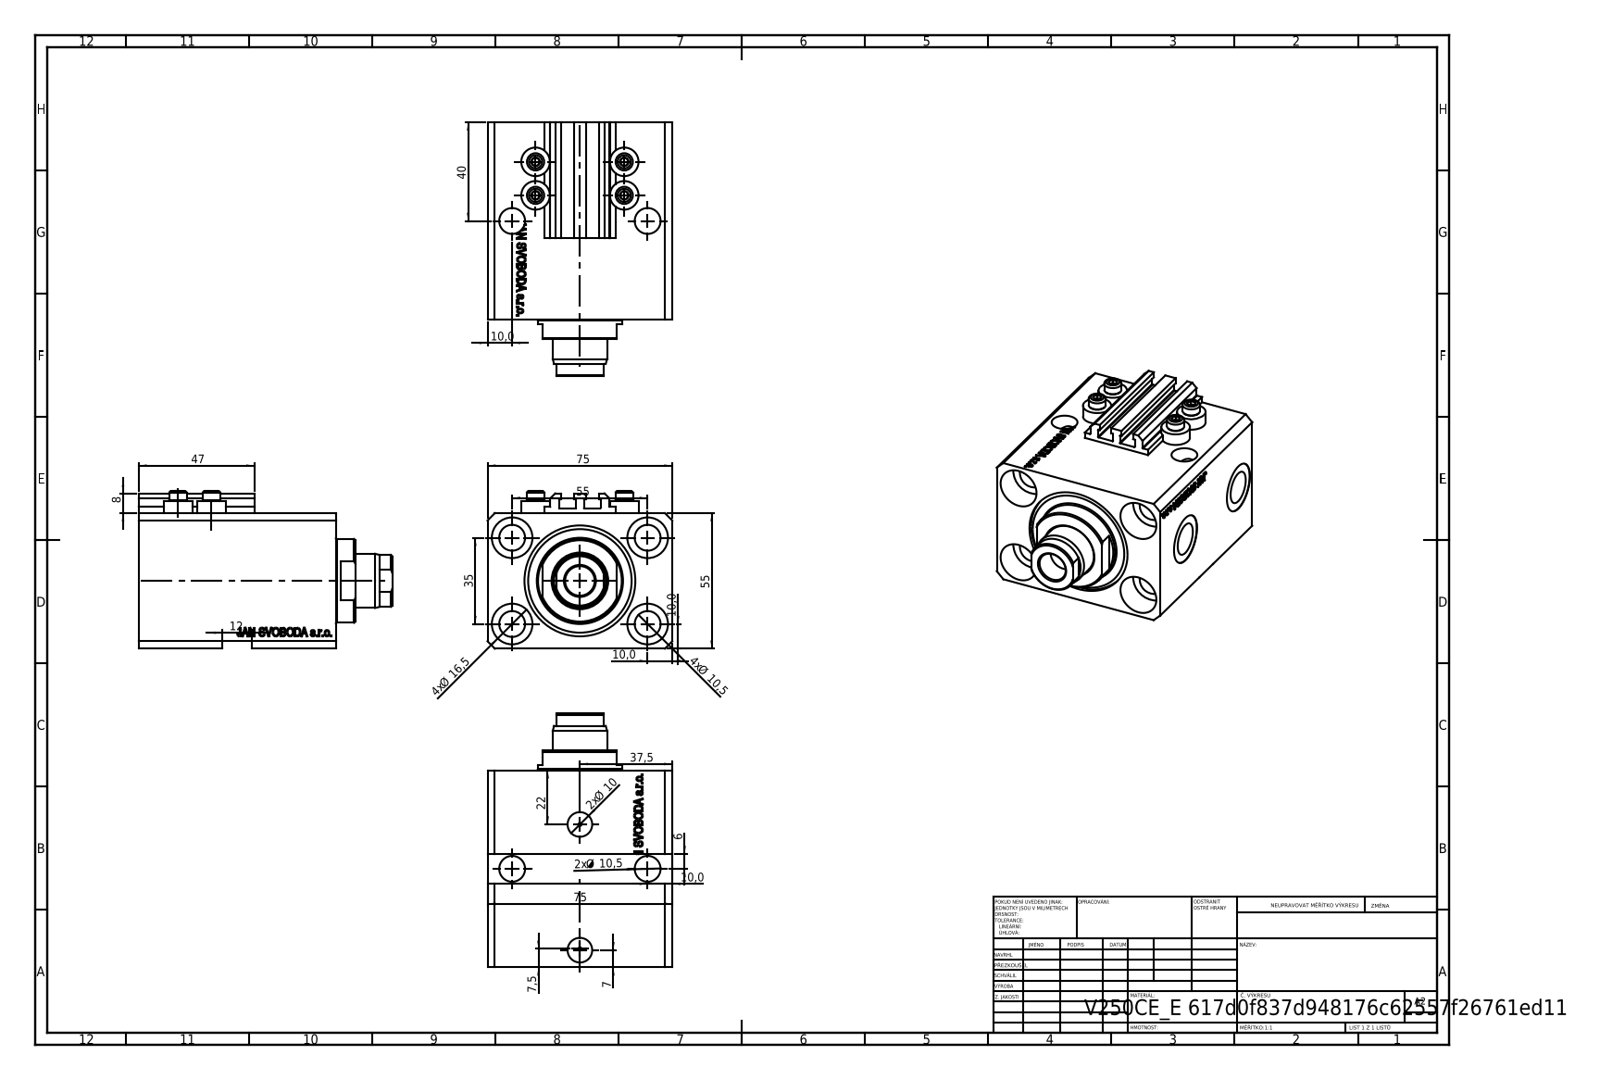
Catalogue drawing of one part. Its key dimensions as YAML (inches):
part_name: "V250CE_E; V250CE_E_vnitrni cast pro vysunuti; V250CE_C_VCP; ALLEN BOLT V250CE"
step_written_by: "SolidWorks 2019 (CONFIG_CONTROL_DESIGN)"
units: inches
bodies: {solids: 7, faces: 1061, planar: 517, cylindrical: 124, other: 420}
overall_size: [4.055, 2.953, 2.52]
volume: 17.58
surface_area: 109.9
round_holes:
  - {diameter: 0.413, count: 6}
  - {diameter: 0.049, count: 4}
  - {diameter: 0.157, count: 4}
  - {diameter: 0.65, count: 4}
  - {diameter: 0.394, count: 2}
  - {diameter: 0.518, count: 2}
  - {diameter: 0.787, count: 2}
  - {diameter: 0.472, count: 1}
  - {diameter: 0.866, count: 1}
  - {diameter: 1.26, count: 1}
  - {diameter: 1.772, count: 1}
round_bosses_or_shafts:
  - {diameter: 0.457, count: 4}
  - {diameter: 0.276, count: 4}
  - {diameter: 1.339, count: 1}
partial_cylinders:
  - {radius: 0.008, count: 10}
  - {radius: 0.413, count: 1}
face_to_face_distances: [2.165, 2.953, 0.394, 0.472, 2.283, 3.15, 2.677, 0.118, 2.244, 2.756]
hole_center_spacings: [1.283, 2.165, 0.535, 0.555, 0.783, 0.792, 1.016, 1.121]
